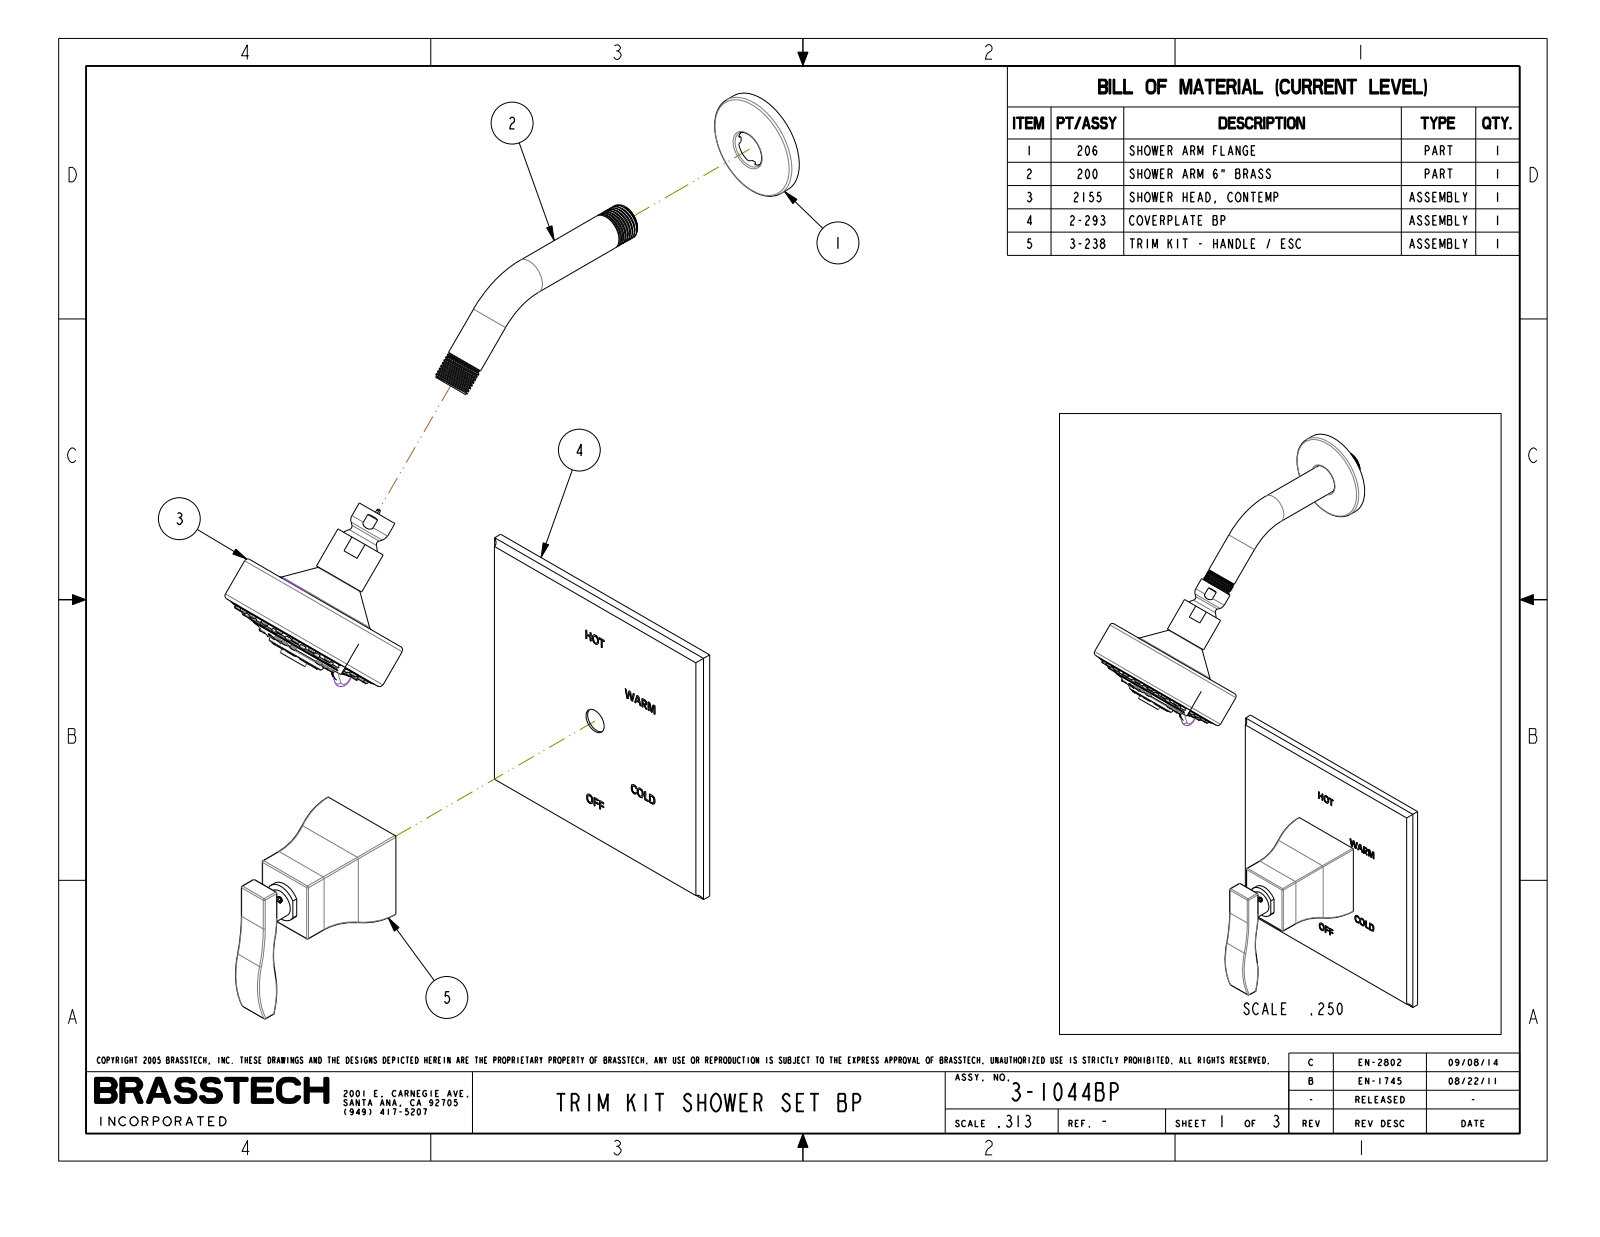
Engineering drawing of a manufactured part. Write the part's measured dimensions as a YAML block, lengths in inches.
part_name: "206; 200; 11375; 50784 (+8 more)"
step_written_by: "PRO/ENGINEER BY PARAMETRIC TECHNOLOGY CORPORATION, 2013150 (CONFIG_CONTROL_DESIGN)"
units: inches
bodies: {solids: 45, faces: 7298, planar: 3273, cylindrical: 1680, other: 2345}
overall_size: [17.44, 8.943, 6.5]
volume: 16.18
surface_area: 634.4
round_holes:
  - {diameter: 0.043, count: 32}
  - {diameter: 0.098, count: 15}
  - {diameter: 0.059, count: 12}
  - {diameter: 0.079, count: 8}
  - {diameter: 0.096, count: 8}
  - {diameter: 0.187, count: 8}
  - {diameter: 0.118, count: 7}
  - {diameter: 0.15, count: 3}
  - {diameter: 0.252, count: 3}
  - {diameter: 0.276, count: 3}
  - {diameter: 0.13, count: 2}
  - {diameter: 0.268, count: 2}
round_bosses_or_shafts:
  - {diameter: 0.142, count: 39}
  - {diameter: 0.165, count: 23}
  - {diameter: 0.315, count: 3}
  - {diameter: 0.244, count: 3}
  - {diameter: 0.813, count: 2}
  - {diameter: 0.768, count: 2}
  - {diameter: 0.63, count: 2}
  - {diameter: 0.228, count: 2}
partial_cylinders:
  - {radius: 0.02, count: 52}
  - {radius: 0.03, count: 30}
  - {radius: 0.012, count: 29}
  - {radius: 0.083, count: 15}
  - {radius: 0.007, count: 14}
  - {radius: 0.063, count: 12}
  - {radius: 0.079, count: 10}
  - {radius: 0.087, count: 8}
face_to_face_distances: [0.05, 0.098, 0.209, 0.698, 0.04, 0.287, 0.307, 0.658, 0.45, 0.49]
hole_center_spacings: [0.378, 0.274, 0.421, 0.37, 0.607, 0.239, 0.782, 0.786]
